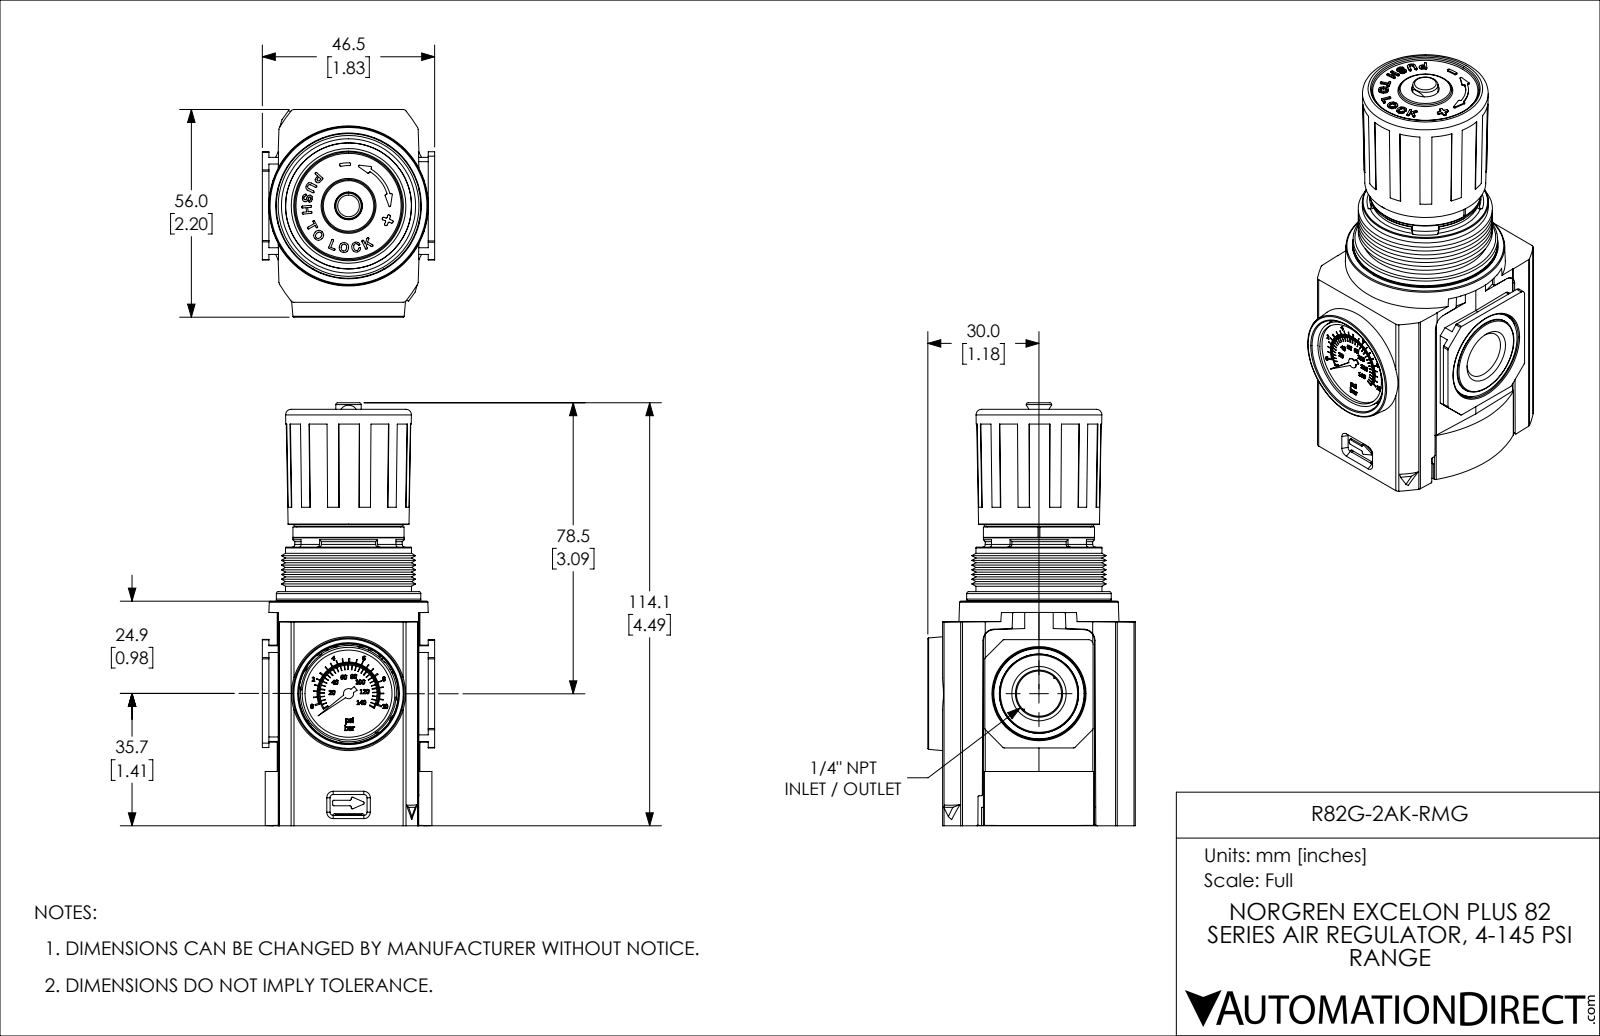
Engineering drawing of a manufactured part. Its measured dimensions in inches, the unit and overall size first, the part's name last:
Units: inches
Overall size (bounding box): 4.492 × 2.205 × 1.831
Round holes (diameter × count): ⌀0.097 ×4, ⌀0.138 ×2, ⌀0.128 ×1, ⌀0.197 ×1, ⌀0.236 ×1, ⌀0.886 ×1, ⌀0.925 ×1, ⌀1.102 ×1, ⌀1.354 ×1
Round bosses / shafts (diameter × count): ⌀0.224 ×2, ⌀0.118 ×2, ⌀1.535 ×1, ⌀1.339 ×1, ⌀1.181 ×1, ⌀1.161 ×1, ⌀1.138 ×1, ⌀1.098 ×1
Partial cylindrical surfaces — rounded edges, fillets, slot ends (radius × count): R0.039 ×68, R0.02 ×39, R0.009 ×25, R0.031 ×20, R0.006 ×12, R0.012 ×12, R0.012 ×12, R0.031 ×12
Main face-to-face distances: 0.059, 1.988, 0.182, 1.352, 0.354, 1.417, 1.475, 0.123, 1.293, 1.169
Hole centre spacings: 0.63, 1.091, 1.26, 2.705, 3.325, 2.965
Volume: 8.932 in³ · Surface area: 86.75 in²
Bodies: 5 solids, 2163 faces (770 planar, 1066 cylindrical, 327 other)
Part name (STEP PRODUCT): R82G-2AK-RMG
STEP written by: SolidWorks 2021 (CONFIG_CONTROL_DESIGN)
